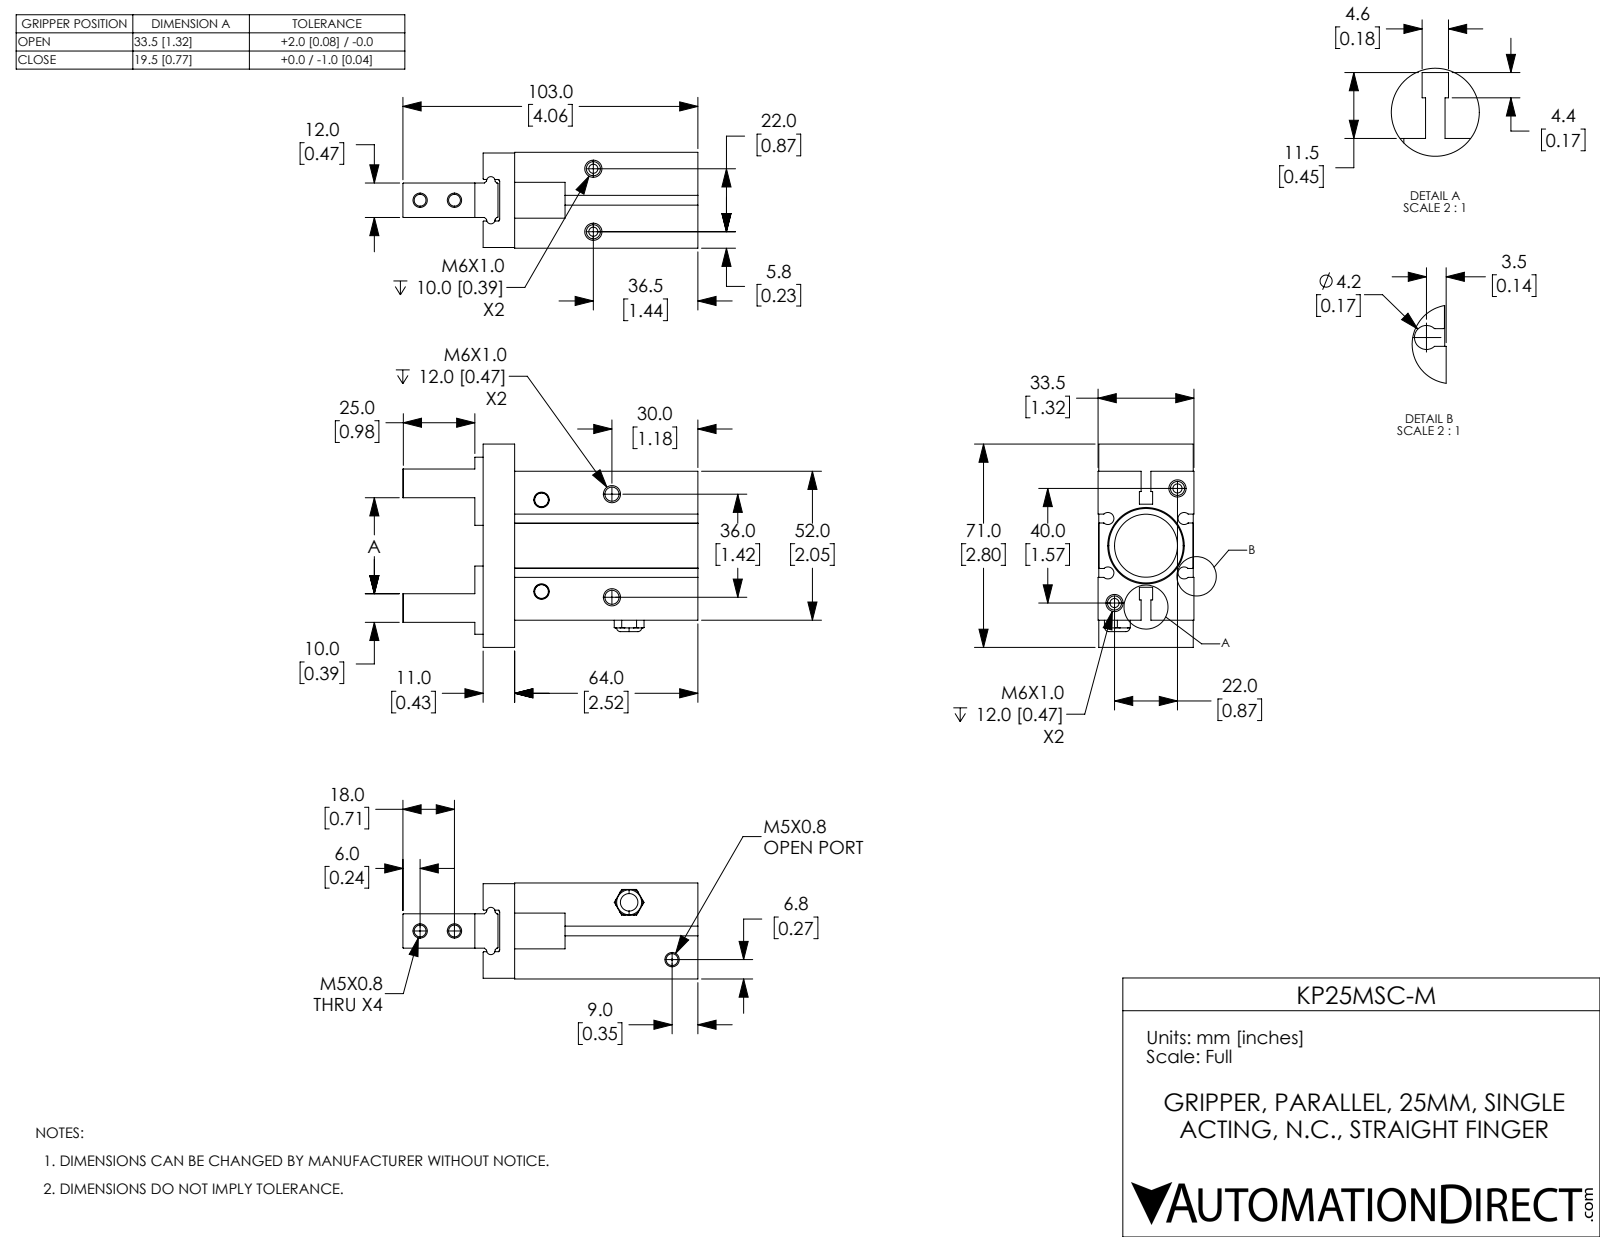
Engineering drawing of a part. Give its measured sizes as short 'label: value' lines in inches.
name: KP25MSC-M-3; KP25MSC-M-1; KP25MSC-M; KP25MSC-M-2
written by: SolidWorks 2017 (CONFIG_CONTROL_DESIGN)
unit: in
bodies: 3 solids, 265 faces (129 planar, 66 cylindrical, 70 other)
size: 4.055 × 2.795 × 1.319
volume: 7.142 in³; area: 51.73 in²
holes: 4× ⌀0.163, 4× ⌀0.194, 2× ⌀0.02, 2× ⌀0.194, 2× ⌀0.237, 1× ⌀0.24, 1× ⌀0.866, 1× ⌀1.024
rounds: 8× R0.008, 4× R0.083, 2× R0.02, 2× R0.059
face distances: 0.413, 0.896, 1.307, 1.319, 0.906, 0.402, 0.894, 0.884, 2.047, 1.309
hole spacings: 0.899, 1.958, 2.421, 0.472, 0.494, 0.866, 0.962, 0.984
